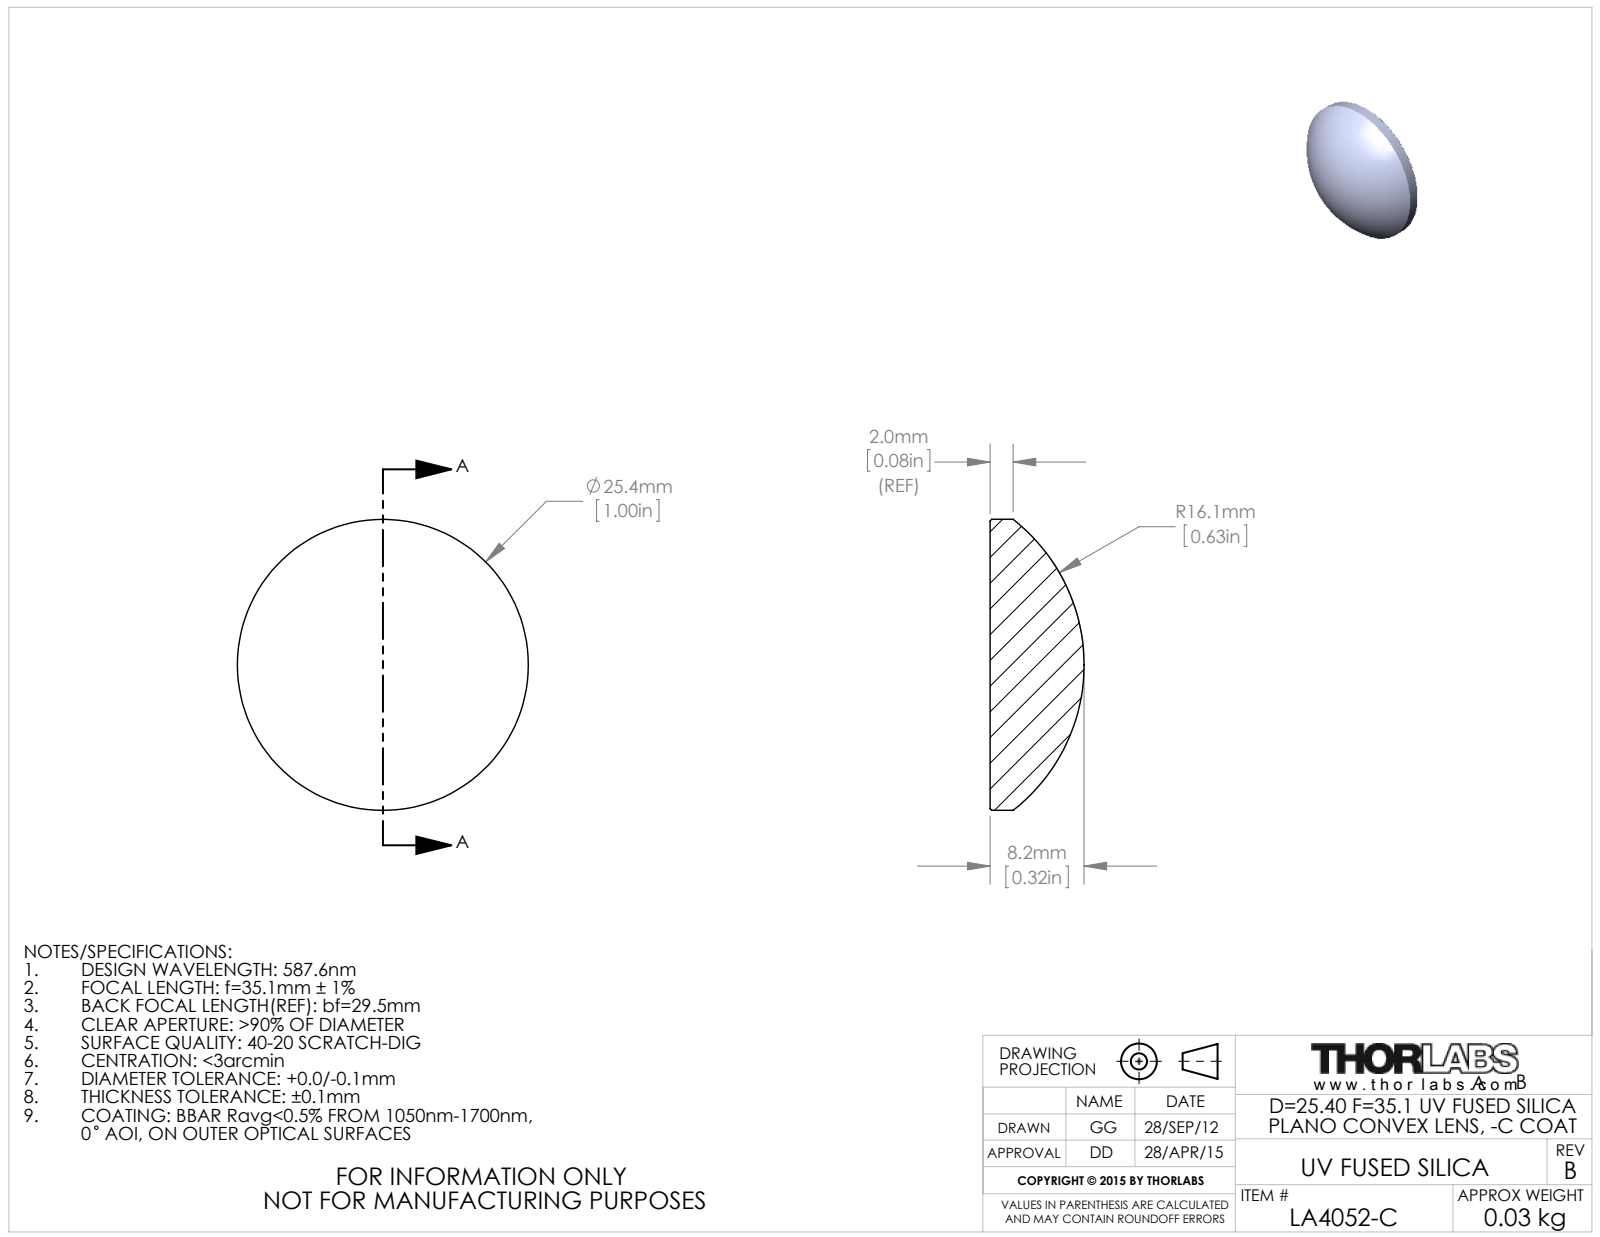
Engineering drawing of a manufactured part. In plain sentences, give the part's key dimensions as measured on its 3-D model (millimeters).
The part is named "24980-E0W". Its 3-D file was written by "SolidWorks 2014 (CONFIG_CONTROL_DESIGN)". It is 1 solid with 7 faces: 1 planar, 2 cylindrical and 4 other. Overall it measures 25.4 by 25.4 by 8.2 millimeters. Its volume is 2 709 cubic millimeters and its surface area 1 287 square millimeters. Round bosses or shafts: 1 of diameter 25.4.
